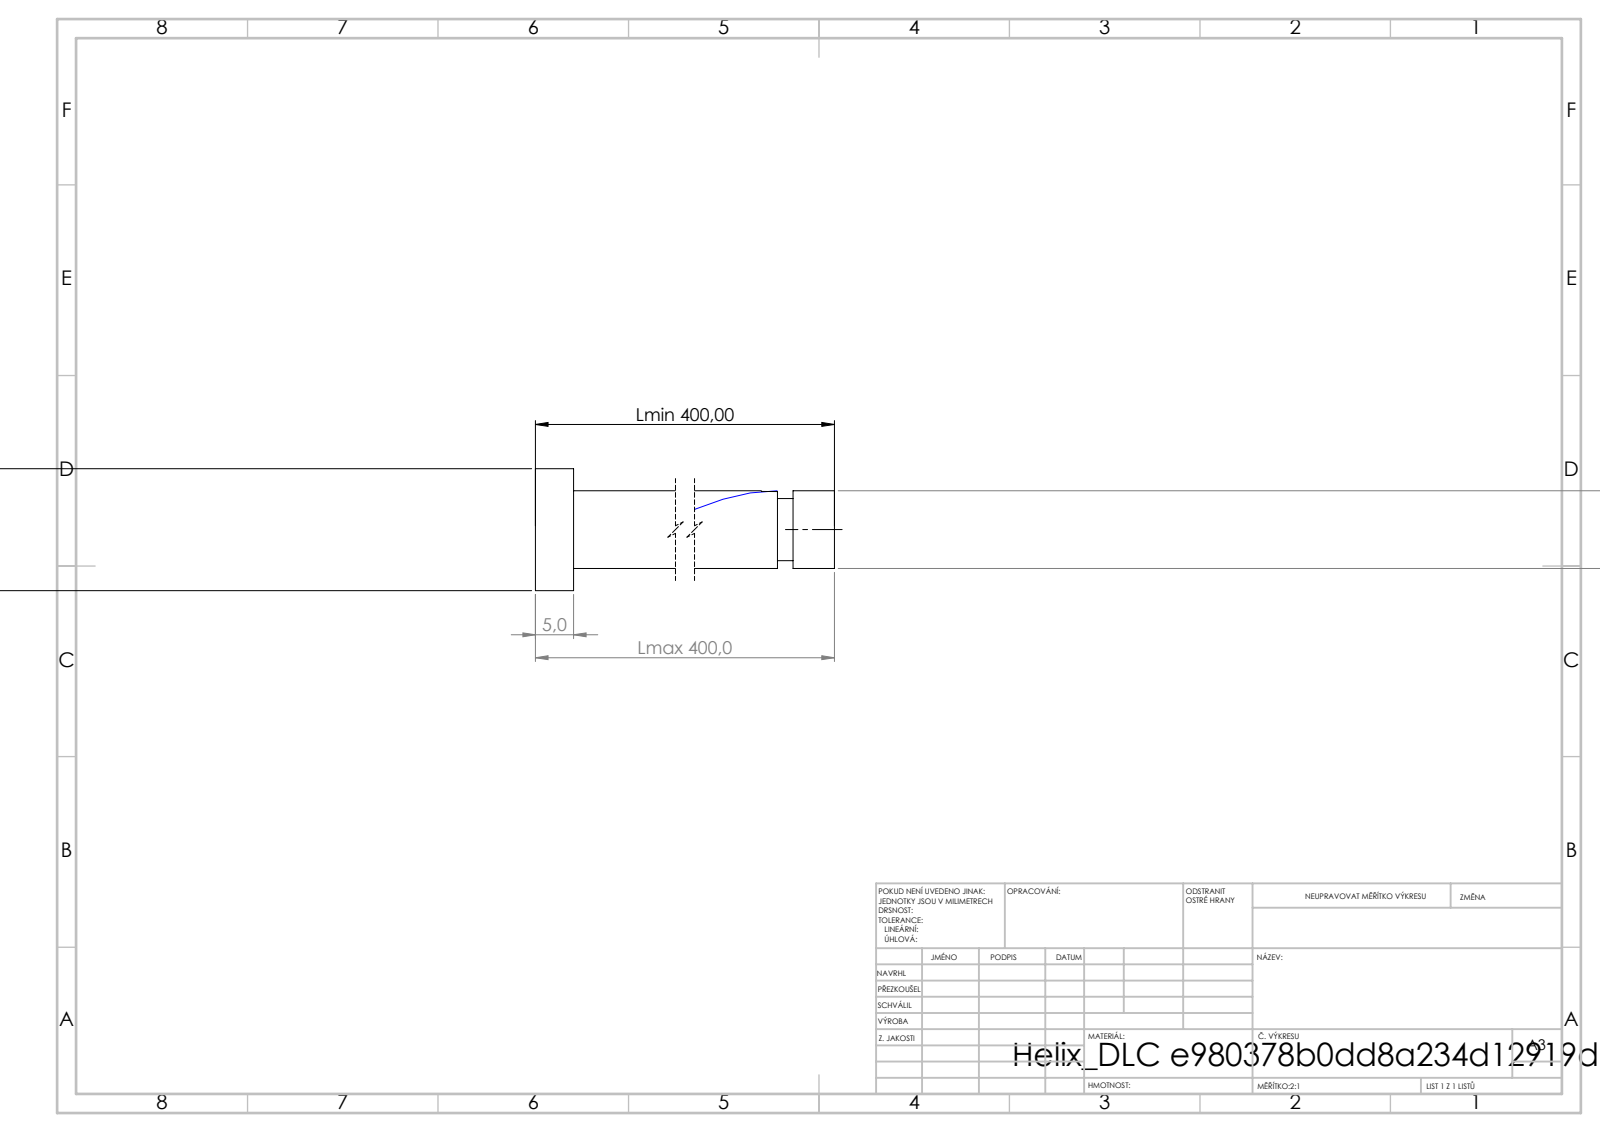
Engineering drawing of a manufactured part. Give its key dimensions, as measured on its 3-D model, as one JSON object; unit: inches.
{"step_written_by": "SolidWorks 2019 (CONFIG_CONTROL_DESIGN)", "units": "inches", "bodies": {"solids": 1, "faces": 21, "planar": 6, "cylindrical": 14, "other": 1}, "overall_size": [15.748, 0.63, 0.63], "volume_in3": 2.008, "surface_area_in2": 21.05, "round_bosses_or_shafts": [[0.63, 1], [0.402, 1], [0.321, 1]], "face_to_face_distances": [0.197, 15.748, 15.551, 15.534, 15.337, 0.214, 15.454, 15.257, 0.08, 0.294]}
